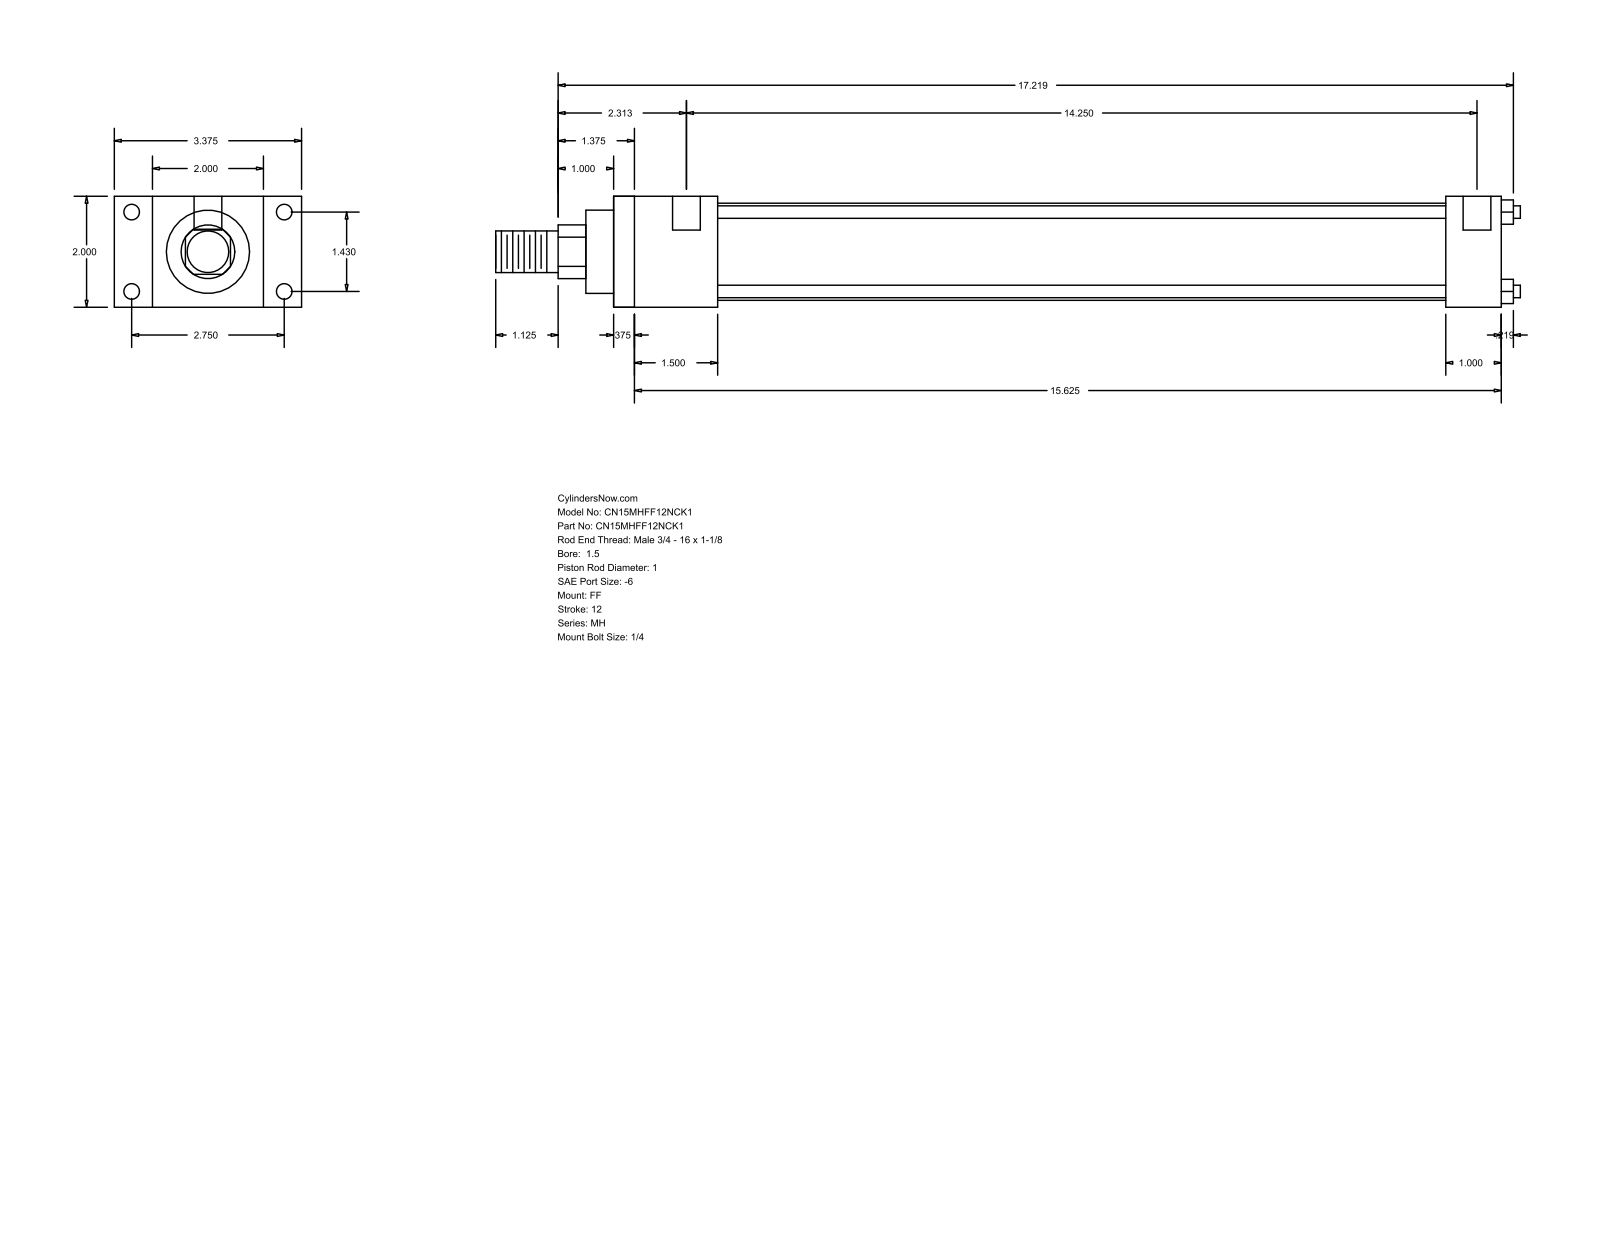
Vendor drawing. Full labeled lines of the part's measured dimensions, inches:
Part name (STEP PRODUCT): MH_FF__0150_1
STEP written by: GSSL Pune (CONFIG_CONTROL_DESIGN)
Units: inches
Bodies: 0 solids, 92 faces (64 planar, 28 cylindrical, 0 other)
Overall size (bounding box): 18.469 × 3.375 × 2
Round holes (diameter × count): ⌀0.219 ×4, ⌀0.281 ×4, ⌀0.5 ×2
Round bosses / shafts (diameter × count): ⌀0.225 ×4, ⌀1.75 ×1, ⌀1.5 ×1, ⌀1 ×1, ⌀0.75 ×1
Partial cylindrical surfaces — rounded edges, fillets, slot ends (radius × count): R0.484 ×1
Main face-to-face distances: 2, 16, 0.375, 15.625, 1, 0.687, 2.687, 1.875, 1.5, 14.125
Hole centre spacings: 1.43, 2.75, 3.099, 14.375, 0.125, 14.25
